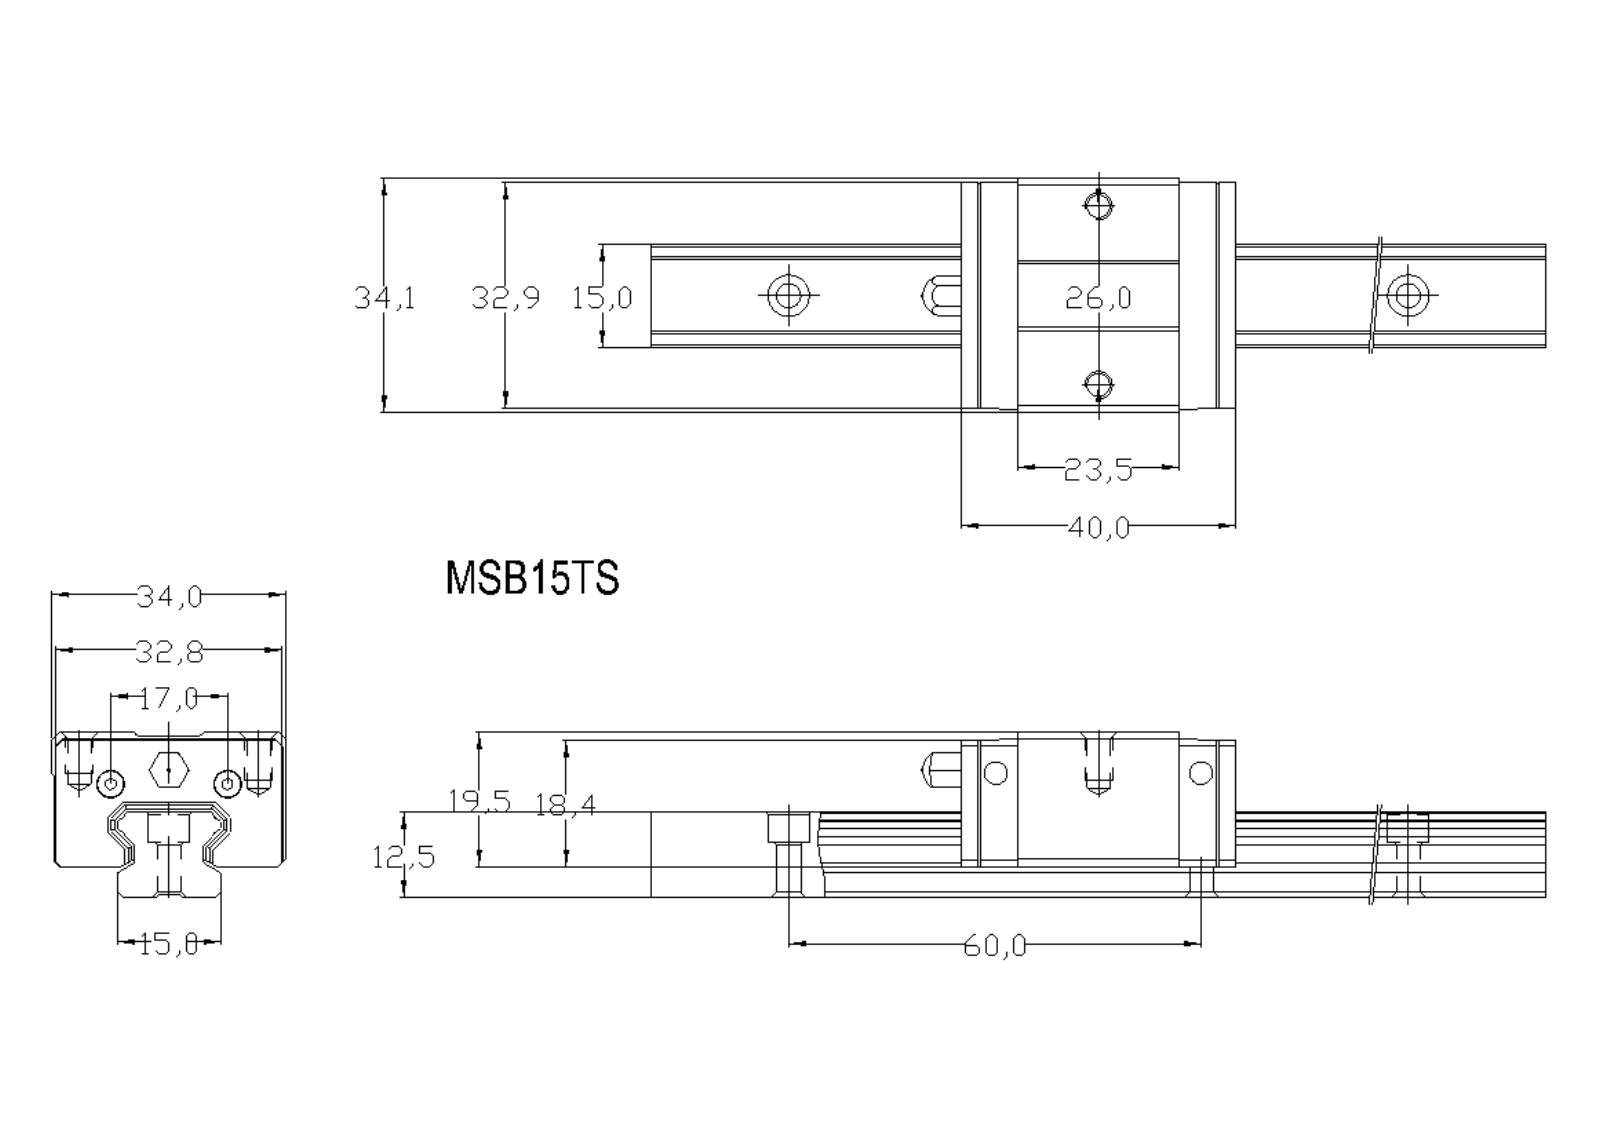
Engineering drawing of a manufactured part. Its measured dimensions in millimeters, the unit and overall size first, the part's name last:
Units: millimetres
Overall size (bounding box): 160 × 34 × 24
Round holes (diameter × count): ⌀4 ×5, ⌀3.5 ×3, ⌀6 ×3
Partial cylindrical surfaces — rounded edges, fillets, slot ends (radius × count): R1.55 ×4, R1 ×2, R3.25 ×1
Main face-to-face distances: 12.5, 2.5, 8, 4.5, 0.6, 8.9, 11.4, 21.4, 23.9, 10
Hole centre spacings: 61.39, 8.73, 13, 60, 17, 26, 120
Volume: 45 416 mm³ · Surface area: 16 948 mm²
Bodies: 3 solids, 145 faces (101 planar, 42 cylindrical, 2 other)
STEP written by: Kubotek KeyCreator V6.5.2 (0407) (CONFIG_CONTROL_DESIGN)
